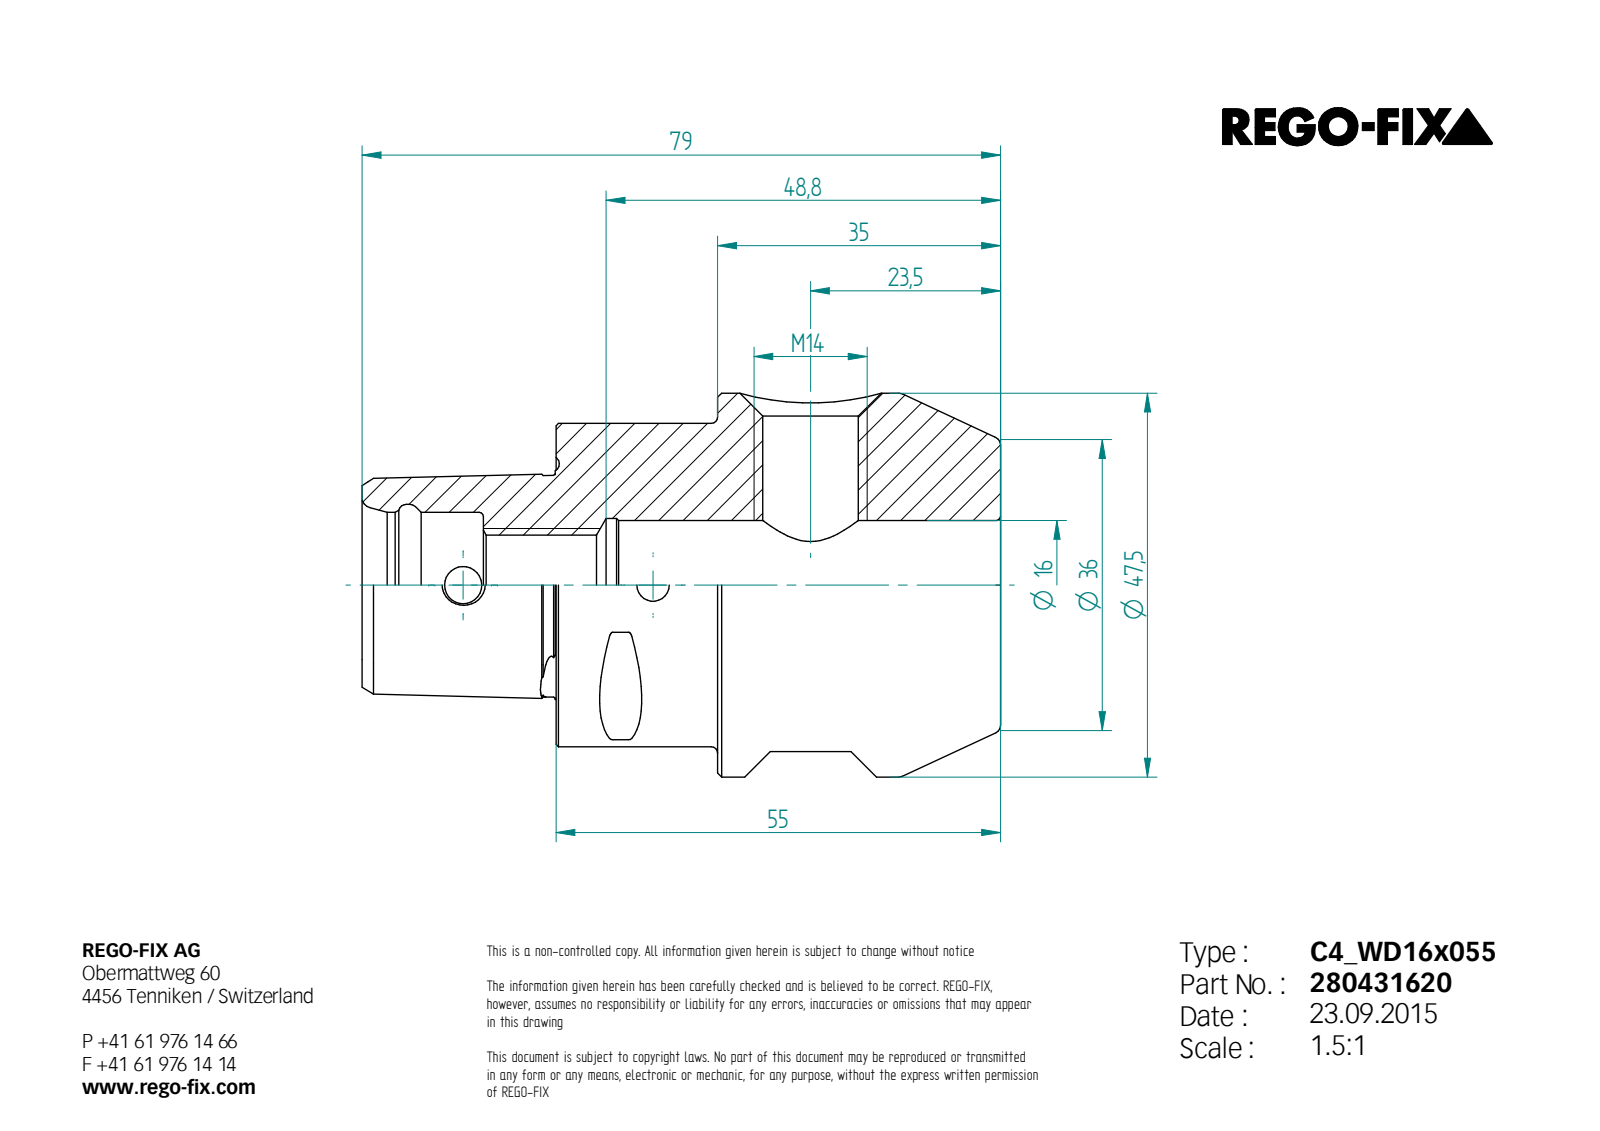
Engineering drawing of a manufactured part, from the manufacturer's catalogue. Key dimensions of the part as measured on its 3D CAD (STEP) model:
STEP written by: Unknown (AUTOMOTIVE_DESIGN)
Units: millimetres
Bodies: 1 solid, 106 faces (23 planar, 20 cylindrical, 63 other)
Overall size (bounding box): 79 × 47.5 × 47.5
Volume: 77 316 mm³ · Surface area: 16 541 mm²
Round holes (diameter × count): ⌀4 ×1, ⌀4.6 ×1, ⌀11.84 ×1, ⌀12.38 ×1, ⌀16 ×1, ⌀16.5 ×1, ⌀18 ×1, ⌀20 ×1
Round bosses / shafts (diameter × count): ⌀47.5 ×1, ⌀40 ×1
Partial cylindrical surfaces — rounded edges, fillets, slot ends (radius × count): R0.5 ×8
Main face-to-face distances: 55, 20, 35, 24, 44, 79, 15.52, 15, 9, 29
Hole centre spacings: 23.5
